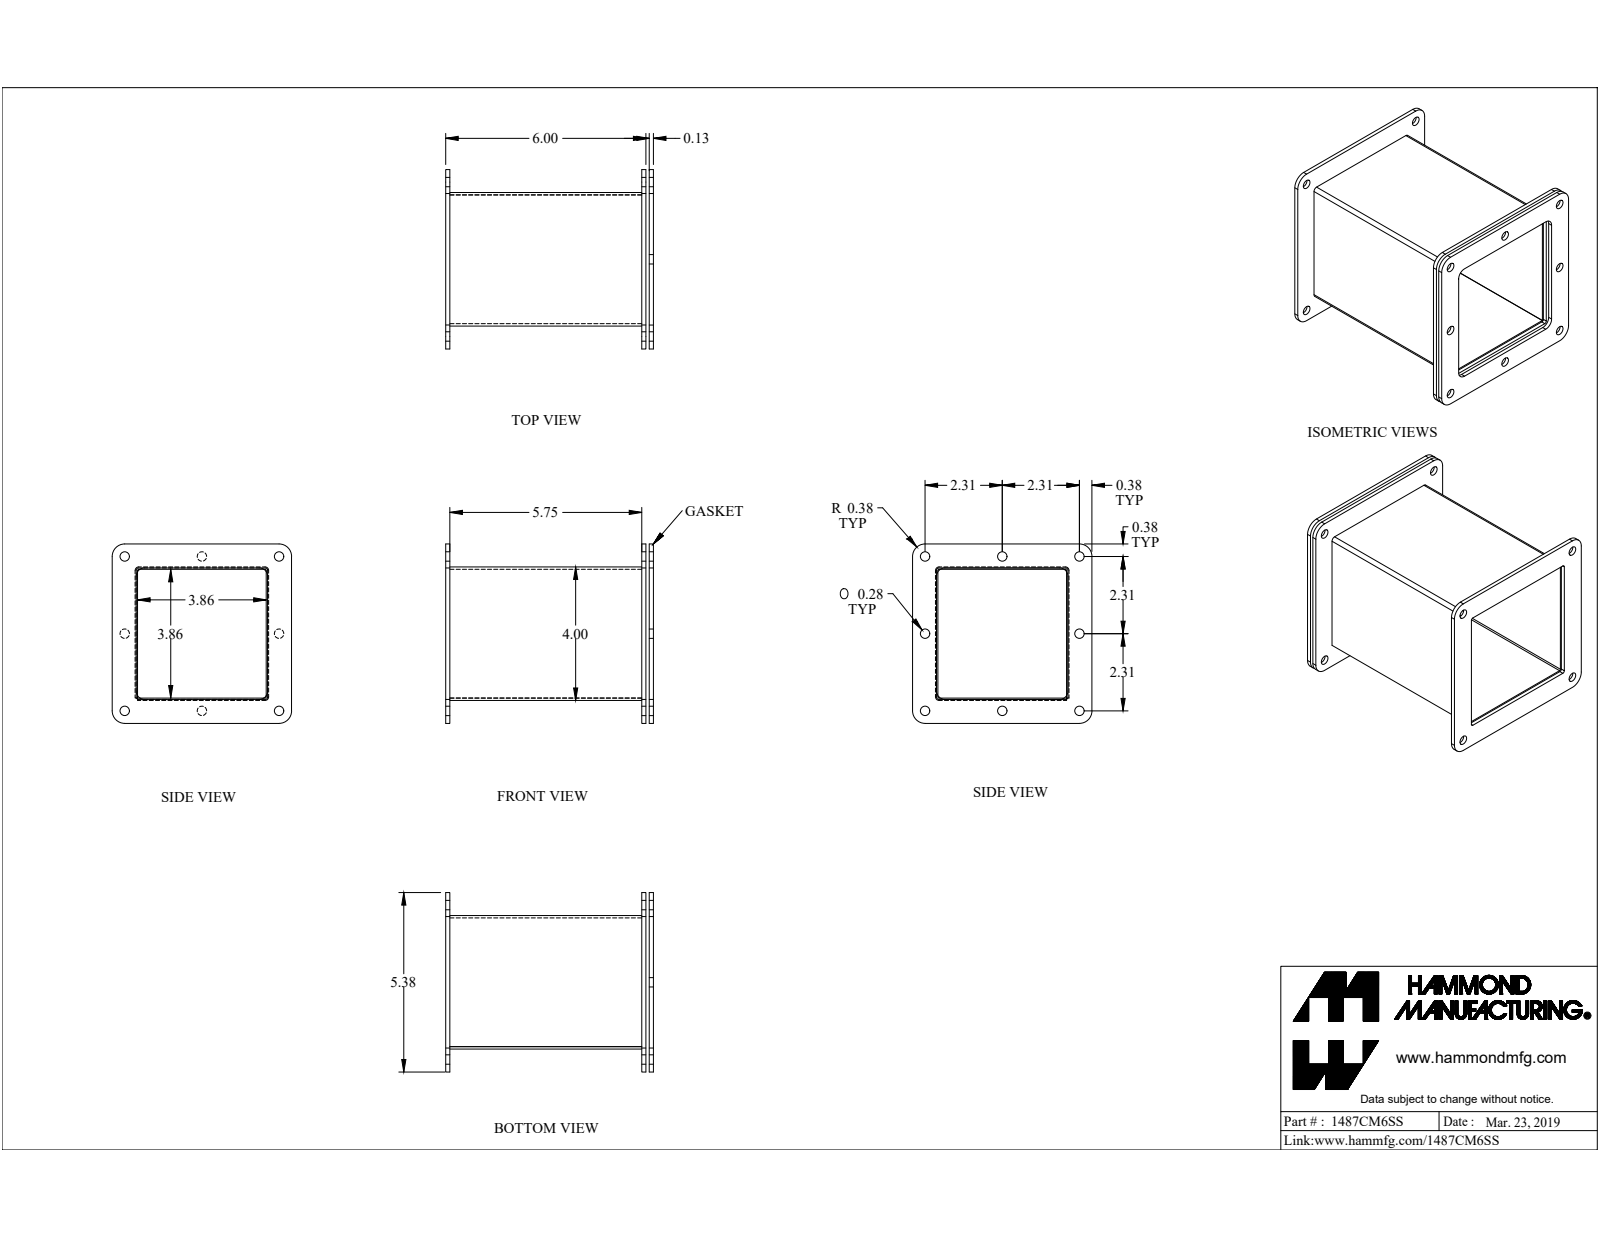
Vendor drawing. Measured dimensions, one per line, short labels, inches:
name: 1487CM6SS
written by: SolidWorks 2019 (CONFIG_CONTROL_DESIGN)
unit: in
bodies: 7 solids, 175 faces (99 planar, 68 cylindrical, 8 other)
size: 6.571 × 5.375 × 5.375
volume: 11.38 in³; area: 277.3 in²
holes: 8× ⌀0.281, 1× ⌀0.196, 1× ⌀0.258, 1× ⌀0.35
bosses: 1× ⌀0.5, 1× ⌀0.25
rounds: 6× R0.02, 4× R0.062, 4× R0.25, 4× R0.375, 3× R0.036, 3× R0.108
face distances: 0.072, 3.928, 4, 3.856, 0.125, 5.875, 0.225, 6.1, 5.75, 6
hole spacings: 2.313, 5.171, 4.625, 3.27, 6.541
